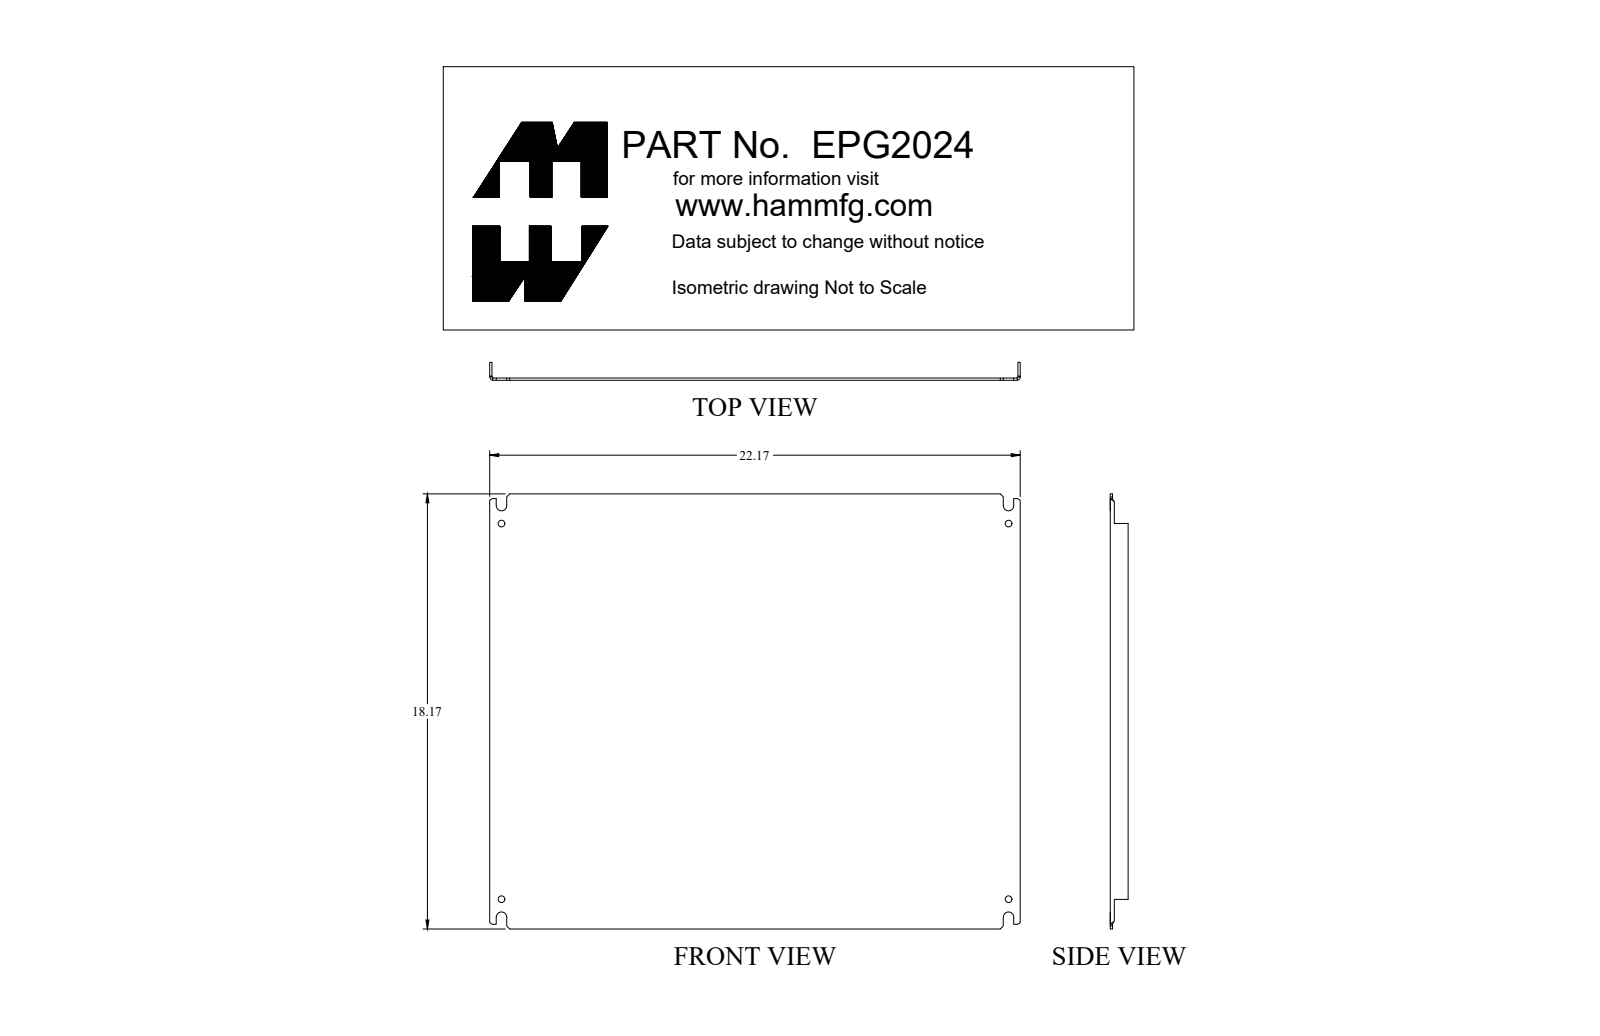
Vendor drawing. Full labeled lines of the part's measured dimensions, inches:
Part name (STEP PRODUCT): EPG2024
STEP written by: SolidWorks 2018 (AUTOMOTIVE_DESIGN)
Units: inches
Bodies: 1 solid, 84 faces (50 planar, 26 cylindrical, 8 other)
Overall size (bounding box): 22.17 × 18.17 × 0.75
Volume: 39.95 in³ · Surface area: 849.5 in²
Round holes (diameter × count): ⌀0.281 ×4
Partial cylindrical surfaces — rounded edges, fillets, slot ends (radius × count): R0.219 ×4, R0.048 ×2, R0.062 ×2, R0.143 ×2
Main face-to-face distances: 0.095, 22.075, 21.98, 22.17, 0.75, 0.655, 18.17, 0.171, 0.076, 0.579
Hole centre spacings: 15.688, 21.188, 26.364
